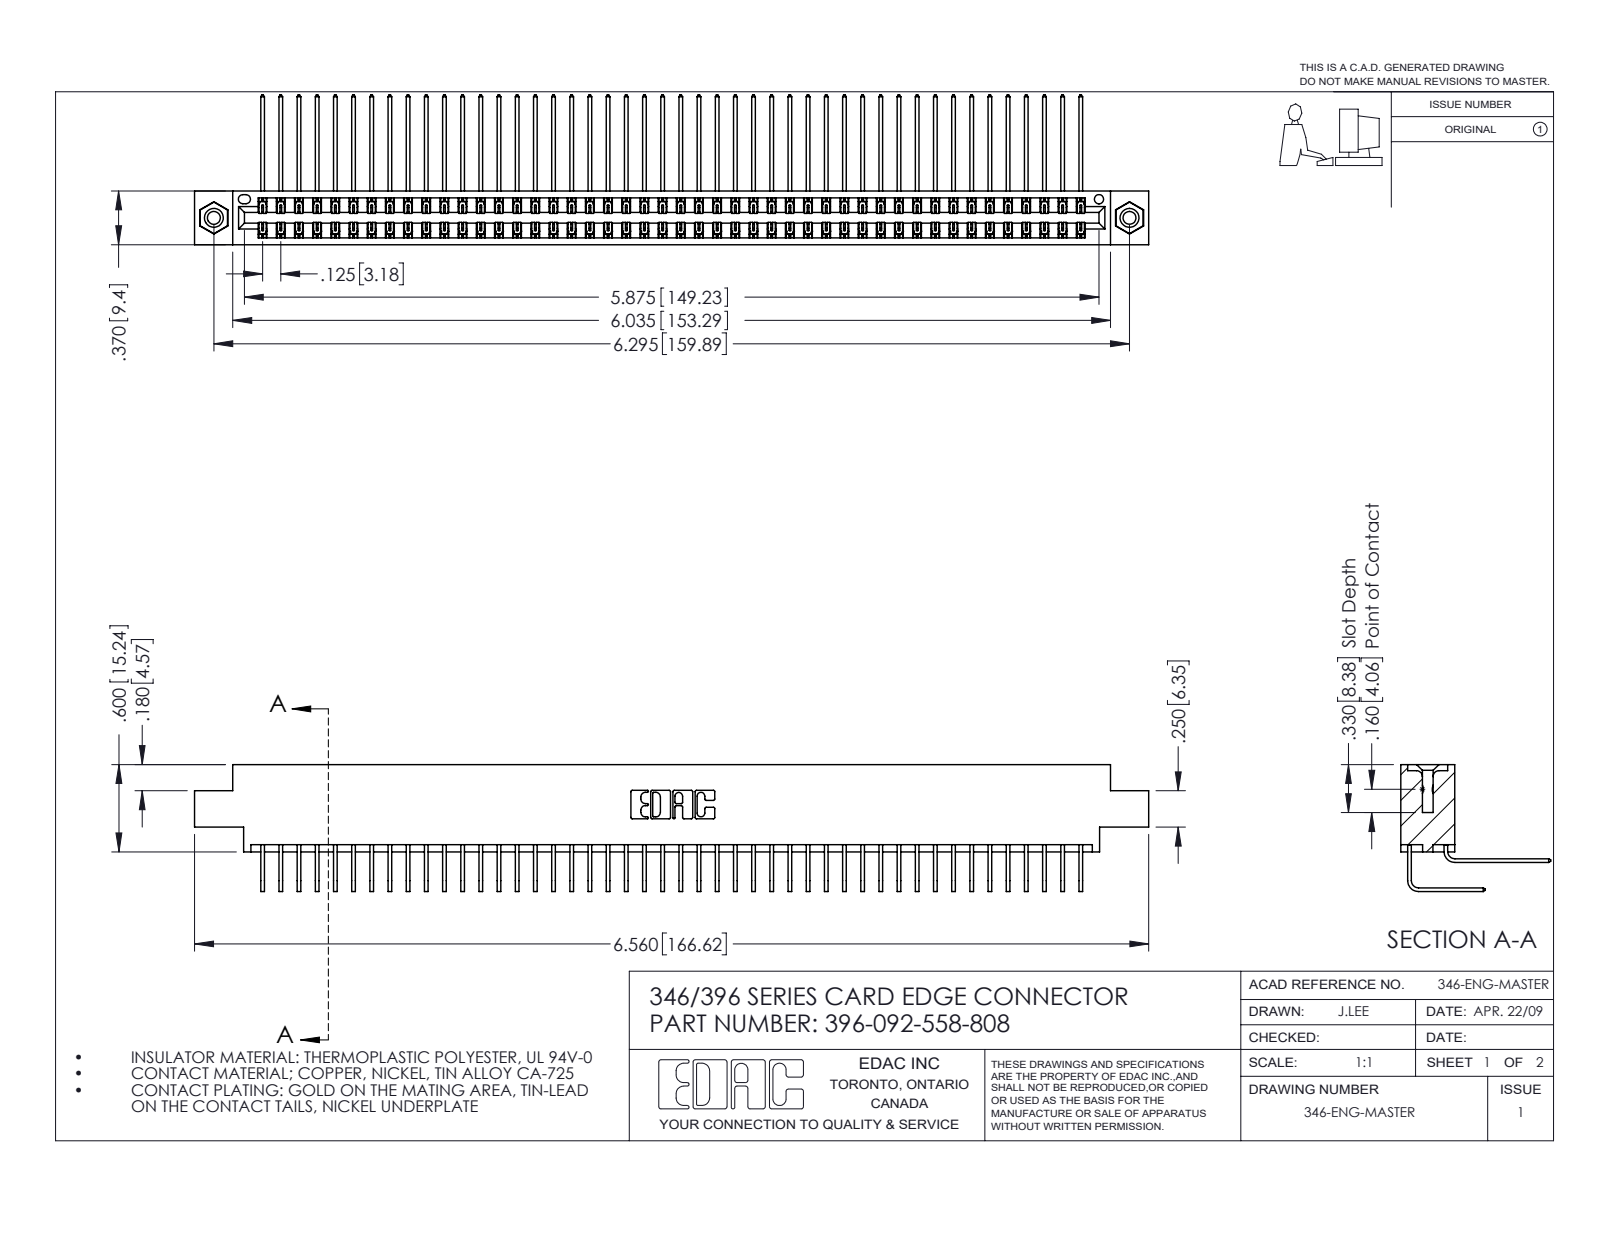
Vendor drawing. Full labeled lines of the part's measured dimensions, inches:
Part name (STEP PRODUCT): 346 Part_0.170 Offset - 0.156 Dia-TI; 345-292-001_558 Tail - 2; 396-092-558-808; 345-250-001_345-250-003-102 (+1 more)
STEP written by: SolidWorks 2016 (CONFIG_CONTROL_DESIGN)
Units: inches
Bodies: 95 solids, 5154 faces (3516 planar, 1622 cylindrical, 16 other)
Overall size (bounding box): 6.56 × 1.03 × 0.873
Volume: 1.016 in³ · Surface area: 39.82 in²
Round holes (diameter × count): ⌀0.089 ×2, ⌀0.125 ×2, ⌀0.156 ×2, ⌀0.064 ×1
Round bosses / shafts (diameter × count): ⌀0.155 ×2
Partial cylindrical surfaces — rounded edges, fillets, slot ends (radius × count): R0.006 ×138, R0.01 ×22, R0.007 ×6, R0.031 ×6, R0.026 ×3, R0.014 ×2, R0.022 ×2, R0.024 ×2
Main face-to-face distances: 0.322, 0.048, 0.025, 0.37, 0.25, 0.298, 0.072, 0.275, 0.222, 0.148
Hole centre spacings: 0.246, 6.086, 6.295
